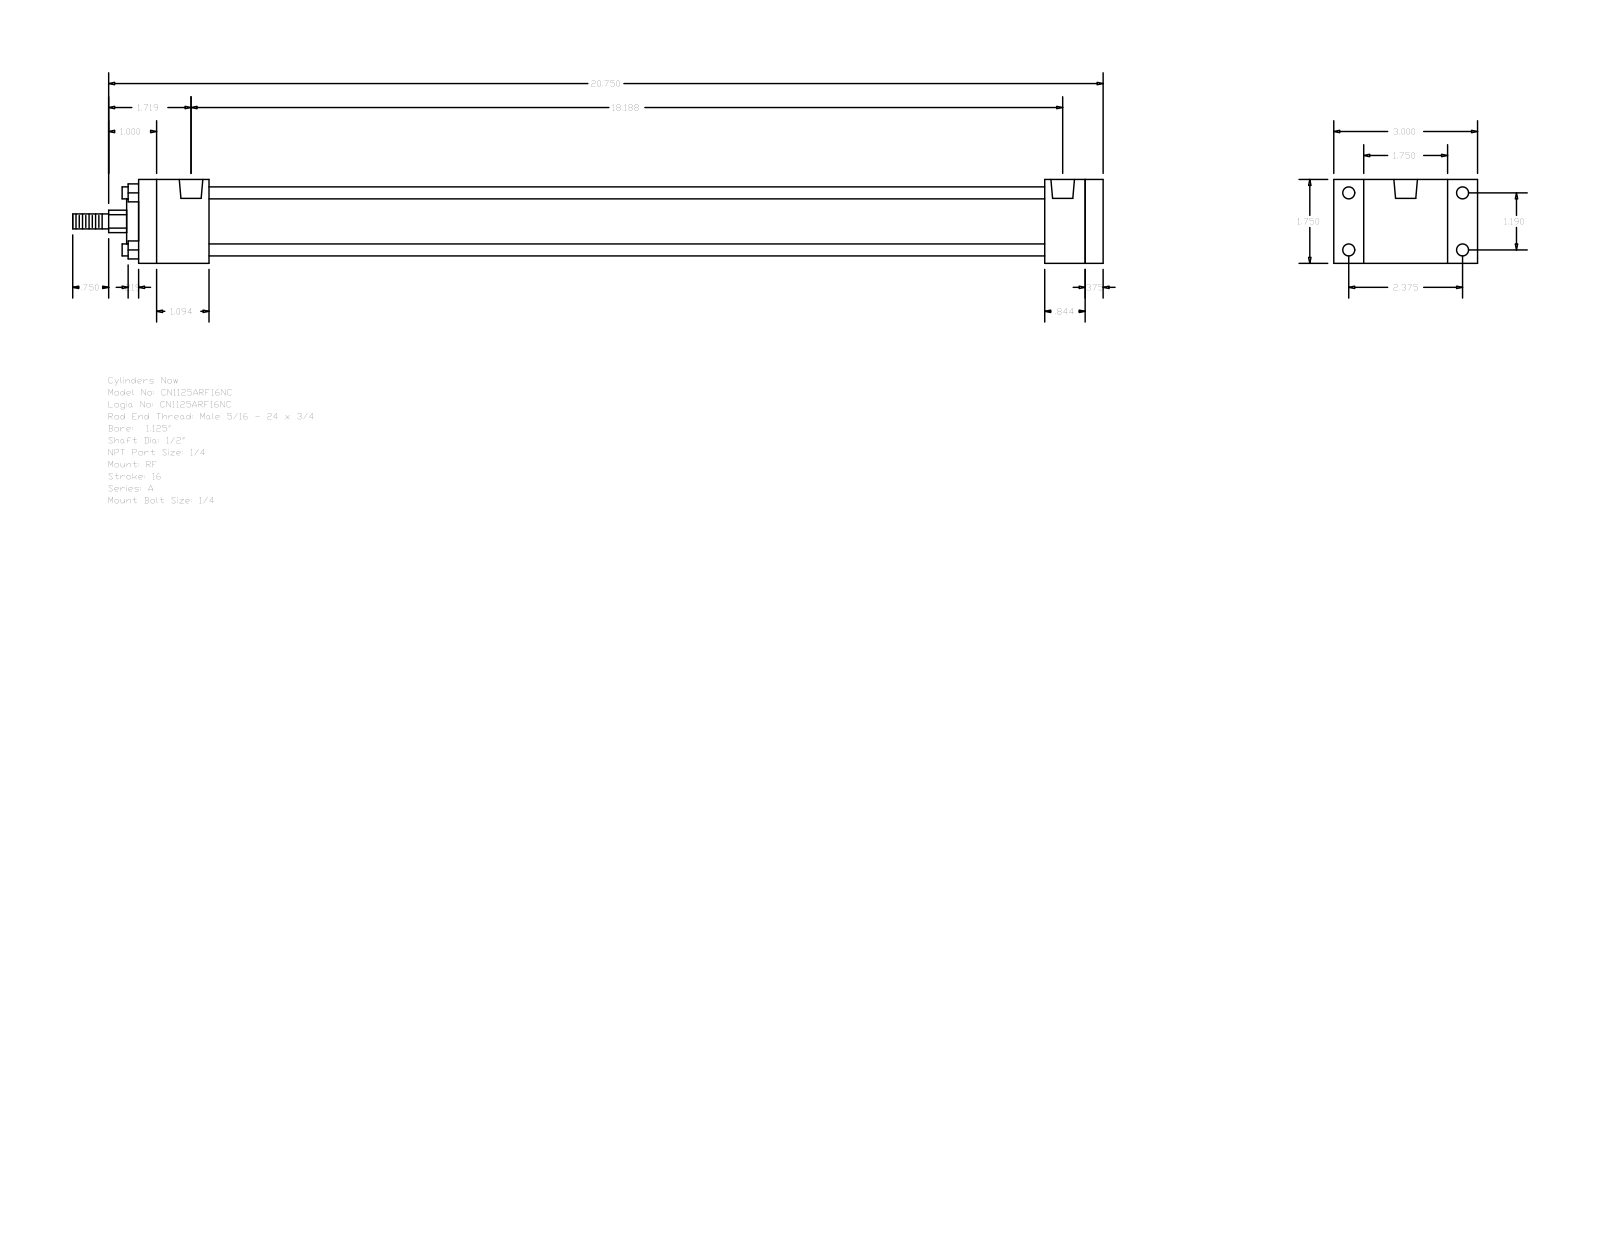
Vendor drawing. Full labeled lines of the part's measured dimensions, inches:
Part name (STEP PRODUCT): A_RF__0112_0.5
STEP written by: GSSL Pune (CONFIG_CONTROL_DESIGN)
Units: inches
Bodies: 0 solids, 92 faces (64 planar, 28 cylindrical, 0 other)
Overall size (bounding box): 21.5 × 3 × 1.75
Round holes (diameter × count): ⌀0.219 ×4, ⌀0.25 ×4, ⌀0.492 ×2
Round bosses / shafts (diameter × count): ⌀0.25 ×4, ⌀1.255 ×1, ⌀0.937 ×1, ⌀0.5 ×1, ⌀0.313 ×1
Partial cylindrical surfaces — rounded edges, fillets, slot ends (radius × count): R0.234 ×1
Main face-to-face distances: 1.75, 0.375, 20.125, 19.75, 1.469, 18.906, 17.437, 18.281, 18.656, 0.844
Hole centre spacings: 1.19, 2.375, 2.656, 18.063, 0.062, 0.063, 18.125, 18.125
